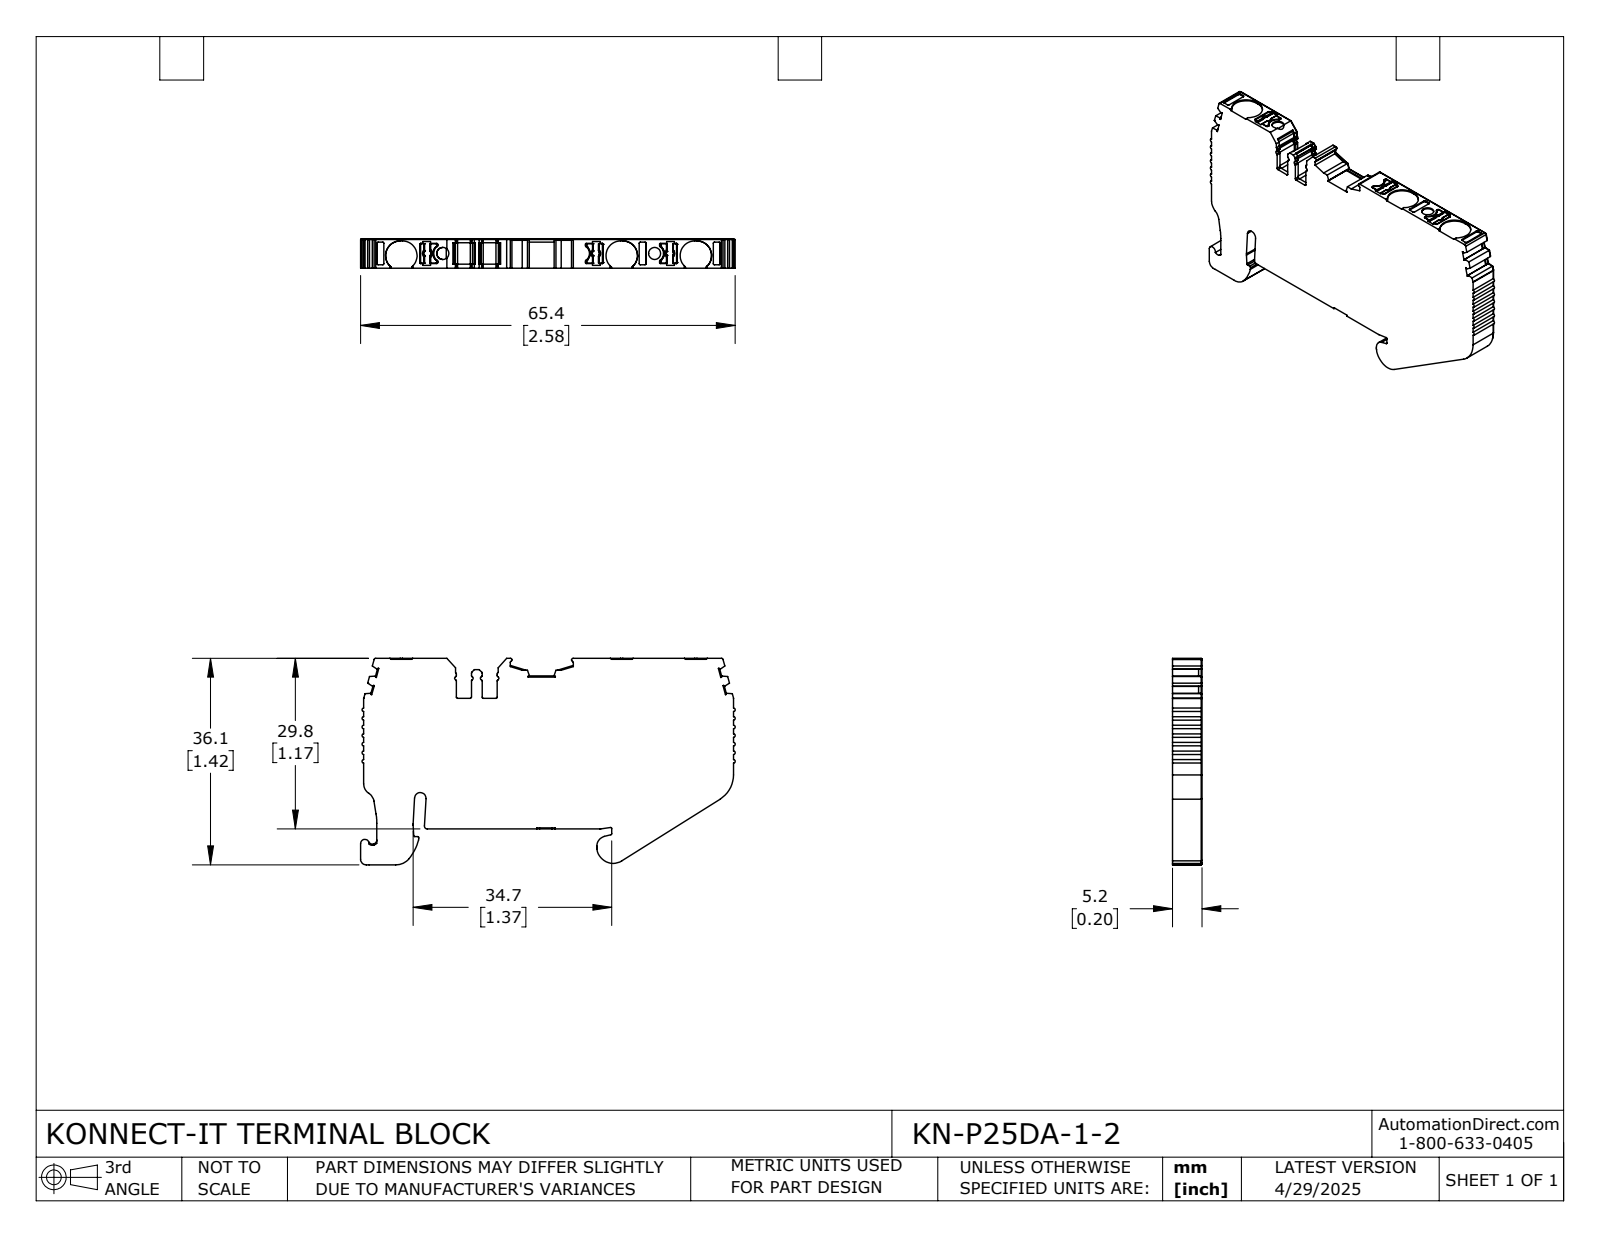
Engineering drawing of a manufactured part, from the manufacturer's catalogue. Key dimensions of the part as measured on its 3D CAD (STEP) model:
Part name (STEP PRODUCT): KN-P25DA-1-2
STEP written by: SolidWorks 2024 (CONFIG_CONTROL_DESIGN)
Units: millimetres
Bodies: 1 solid, 655 faces (345 planar, 259 cylindrical, 51 other)
Overall size (bounding box): 65.42 × 36.07 × 5.15
Volume: 9 576 mm³ · Surface area: 5 140 mm²
Round holes (diameter × count): ⌀2.1 ×2
Partial cylindrical surfaces — rounded edges, fillets, slot ends (radius × count): R0.2 ×66, R0.3 ×39, R0.1 ×19, R0.5 ×18, R0.15 ×12, R0.4 ×9, R2.55 ×6, R1 ×3
Main face-to-face distances: 5.15, 29.61, 29.81, 64.58, 4.5, 5, 6.26, 35.87, 2, 36.07
Hole centre spacings: 36.98
